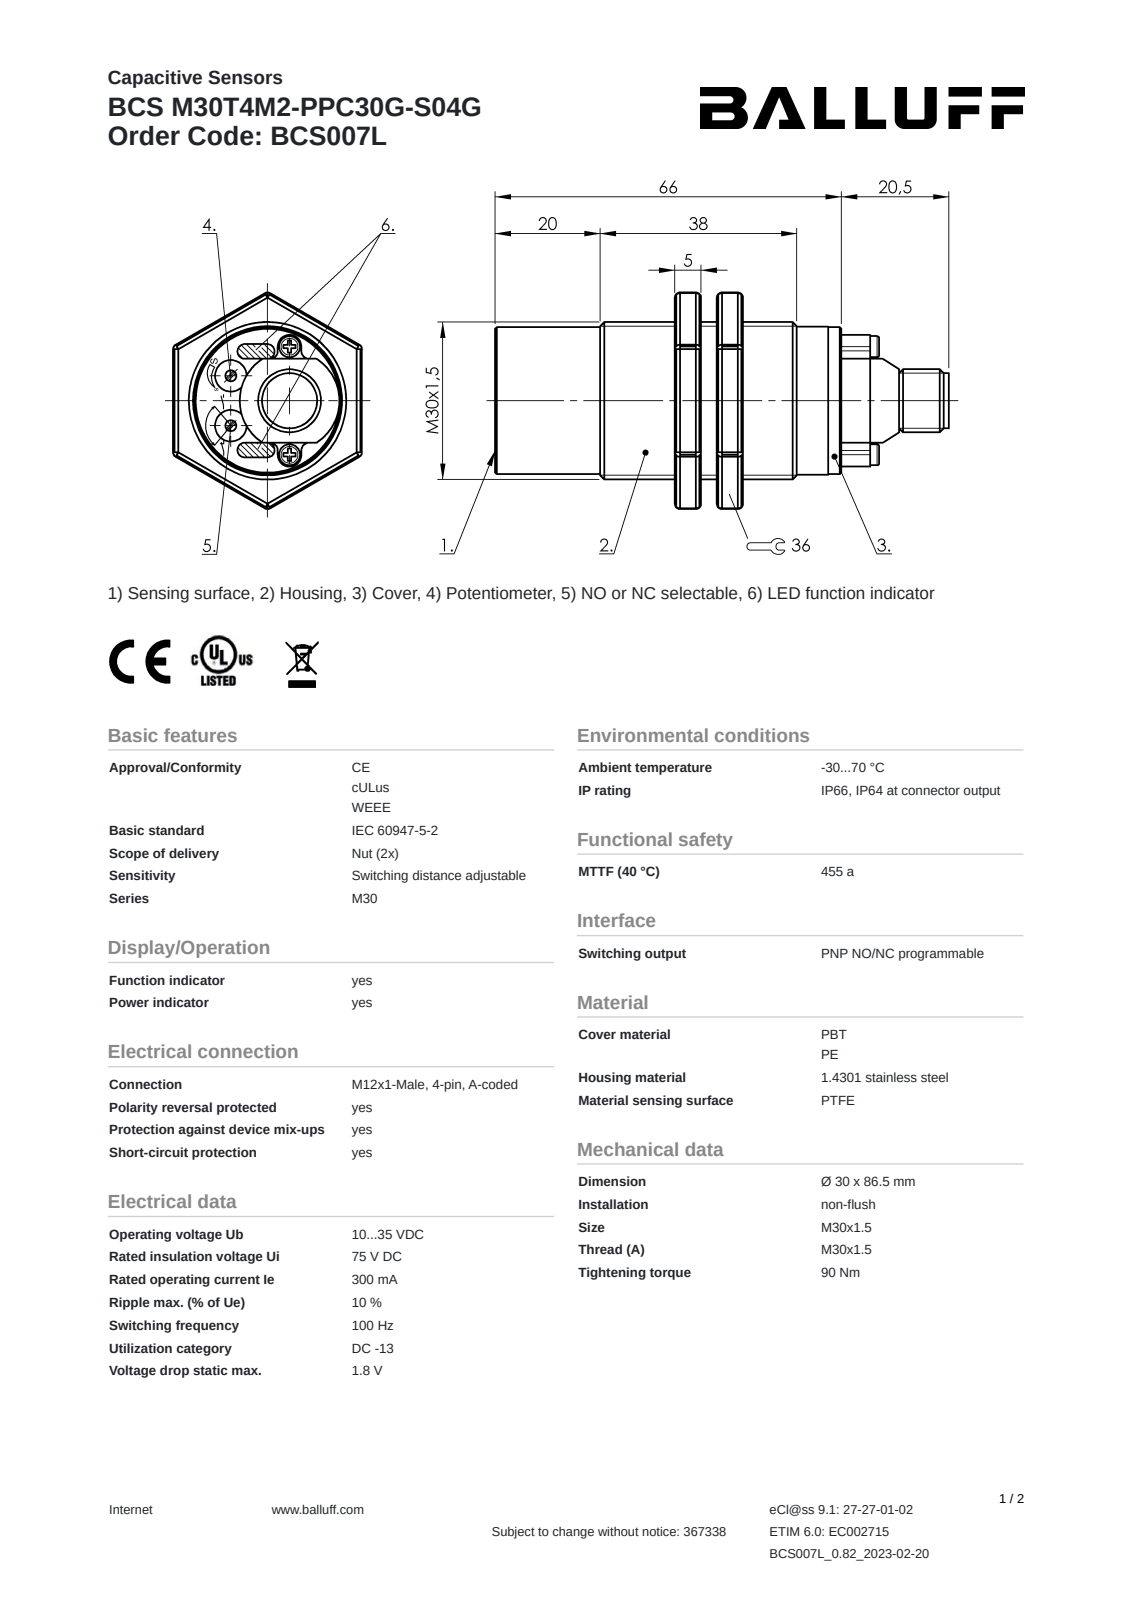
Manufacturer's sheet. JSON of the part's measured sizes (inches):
{"part_name": "BCS007L", "step_written_by": "SolidWorks 2021 (AUTOMOTIVE_DESIGN)", "units": "inches", "bodies": {"solids": 3, "faces": 160, "planar": 87, "cylindrical": 33, "other": 40}, "overall_size": [3.406, 1.637, 1.417], "volume_in3": 3.169, "surface_area_in2": 19.26, "round_holes": [[0.098, 2], [0.197, 2], [0.327, 1], [1.117, 1]], "round_bosses_or_shafts": [[0.039, 4], [0.157, 2], [1.181, 1], [1.102, 1], [1.094, 1], [0.472, 1], [0.409, 1]], "partial_cylinders_radius": [[0.05, 4], [0.059, 4], [0.089, 2], [0.024, 1], [0.363, 1], [0.374, 1]], "face_to_face_distances": [0.315, 0.197, 1.142, 1.417, 1.457, 1.26, 0.945, 0.512, 0.118, 1.339], "hole_center_spacings": [0.333, 0.479, 0.165, 0.374]}
